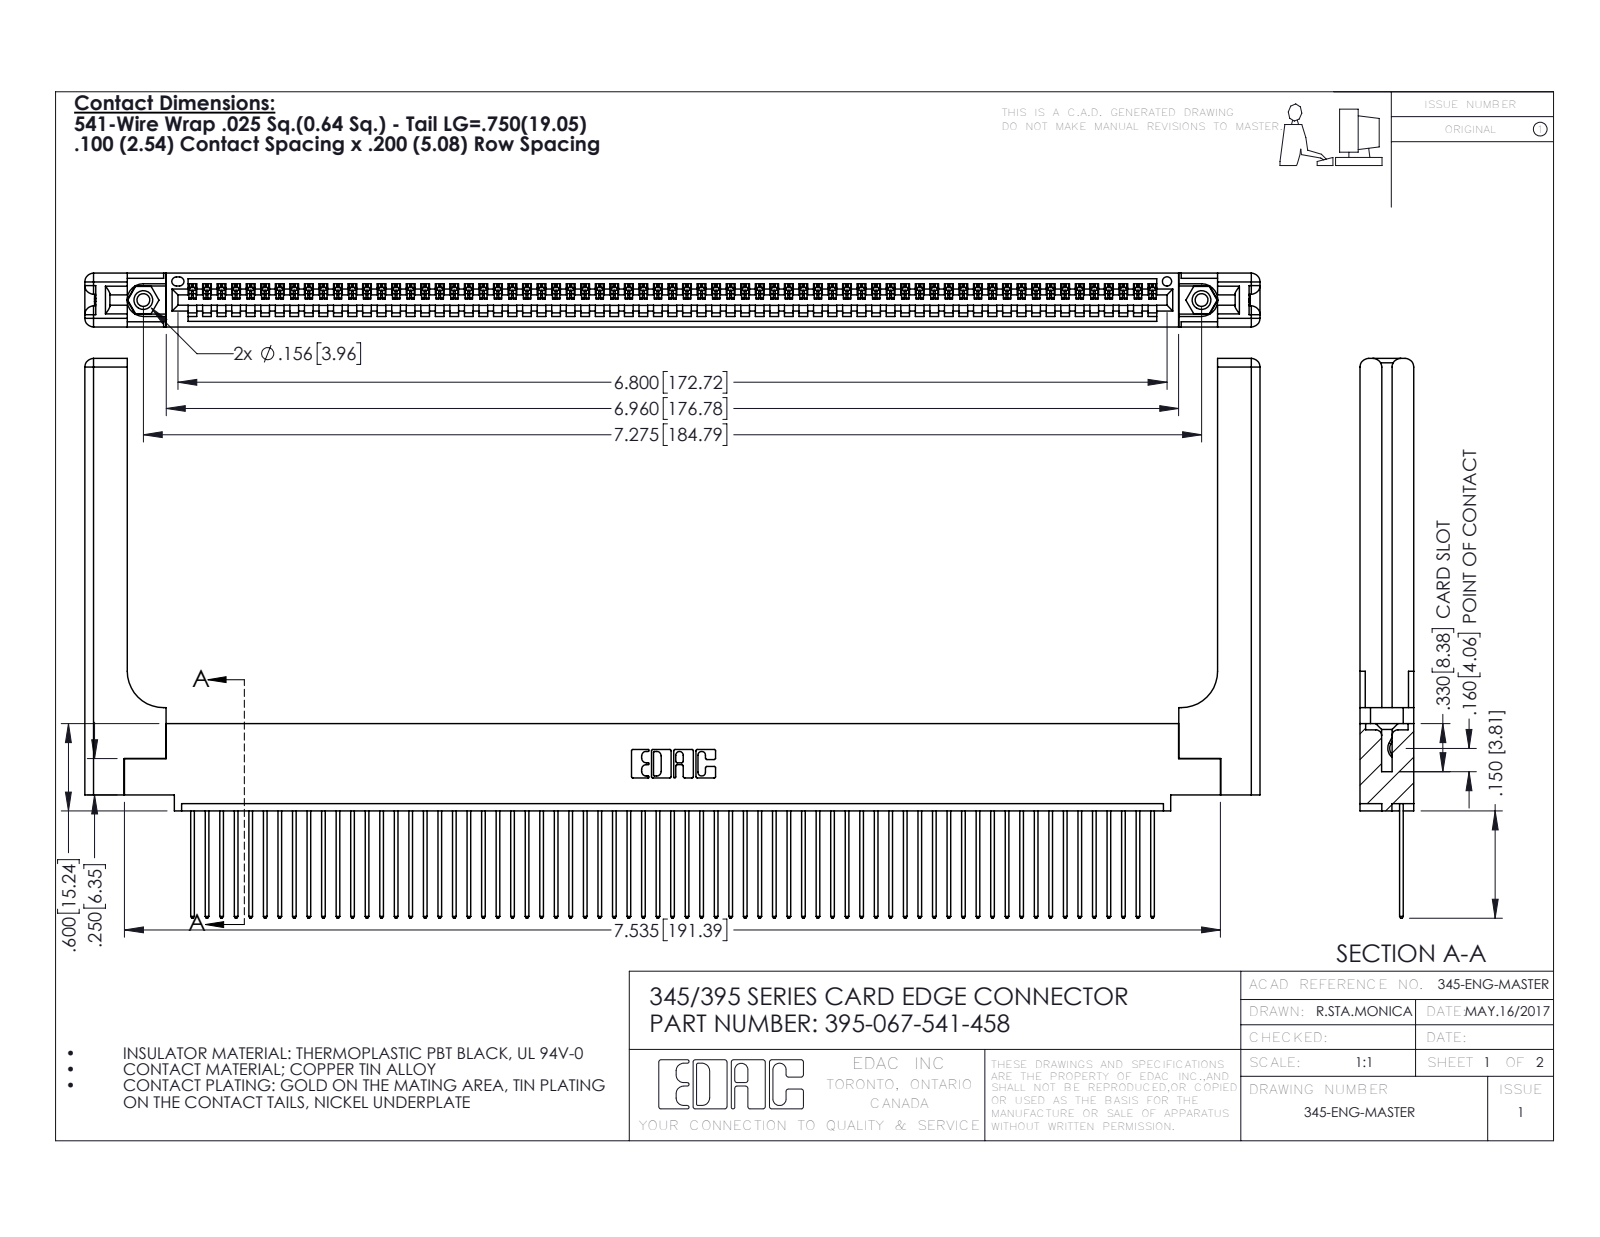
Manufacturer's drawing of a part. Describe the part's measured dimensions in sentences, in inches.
The part is named "345-250-001_345-250-001-102; 345-220-058_345-220-058; 345 Part_0.110 Offset - 0.156 Dia-TH; 395-067-541-458 (+1 more)". Its 3-D file was written by "SolidWorks 2016 (CONFIG_CONTROL_DESIGN)". It is 72 solids with 4272 faces: 2912 planar, 1300 cylindrical and 60 other. Overall it measures 8.079 by 3.847 by 0.37 inches. Its volume is 1.73 cubic inches and its surface area 51.77 square inches. Round holes: 2 of diameter 0.089, 2 of diameter 0.125, 2 of diameter 0.156, 1 of diameter 0.064. Round bosses or shafts: 2 of diameter 0.155. Partial cylindrical surfaces (rounded edges, fillets, slot ends): 134 of radius 0.006, 134 of radius 0.01, 22 of radius 0.01, 16 of radius 0.06, 6 of radius 0.007, 6 of radius 0.031, 3 of radius 0.026, 2 of radius 0.03. The main face-to-face distances are 0.072, 0.298, 0.37, 0.098, 0.272, 0.025, 0.2, 0.225, 0.148, 0.15. The hole center spacings are 0.27, 7.039, 7.275.
